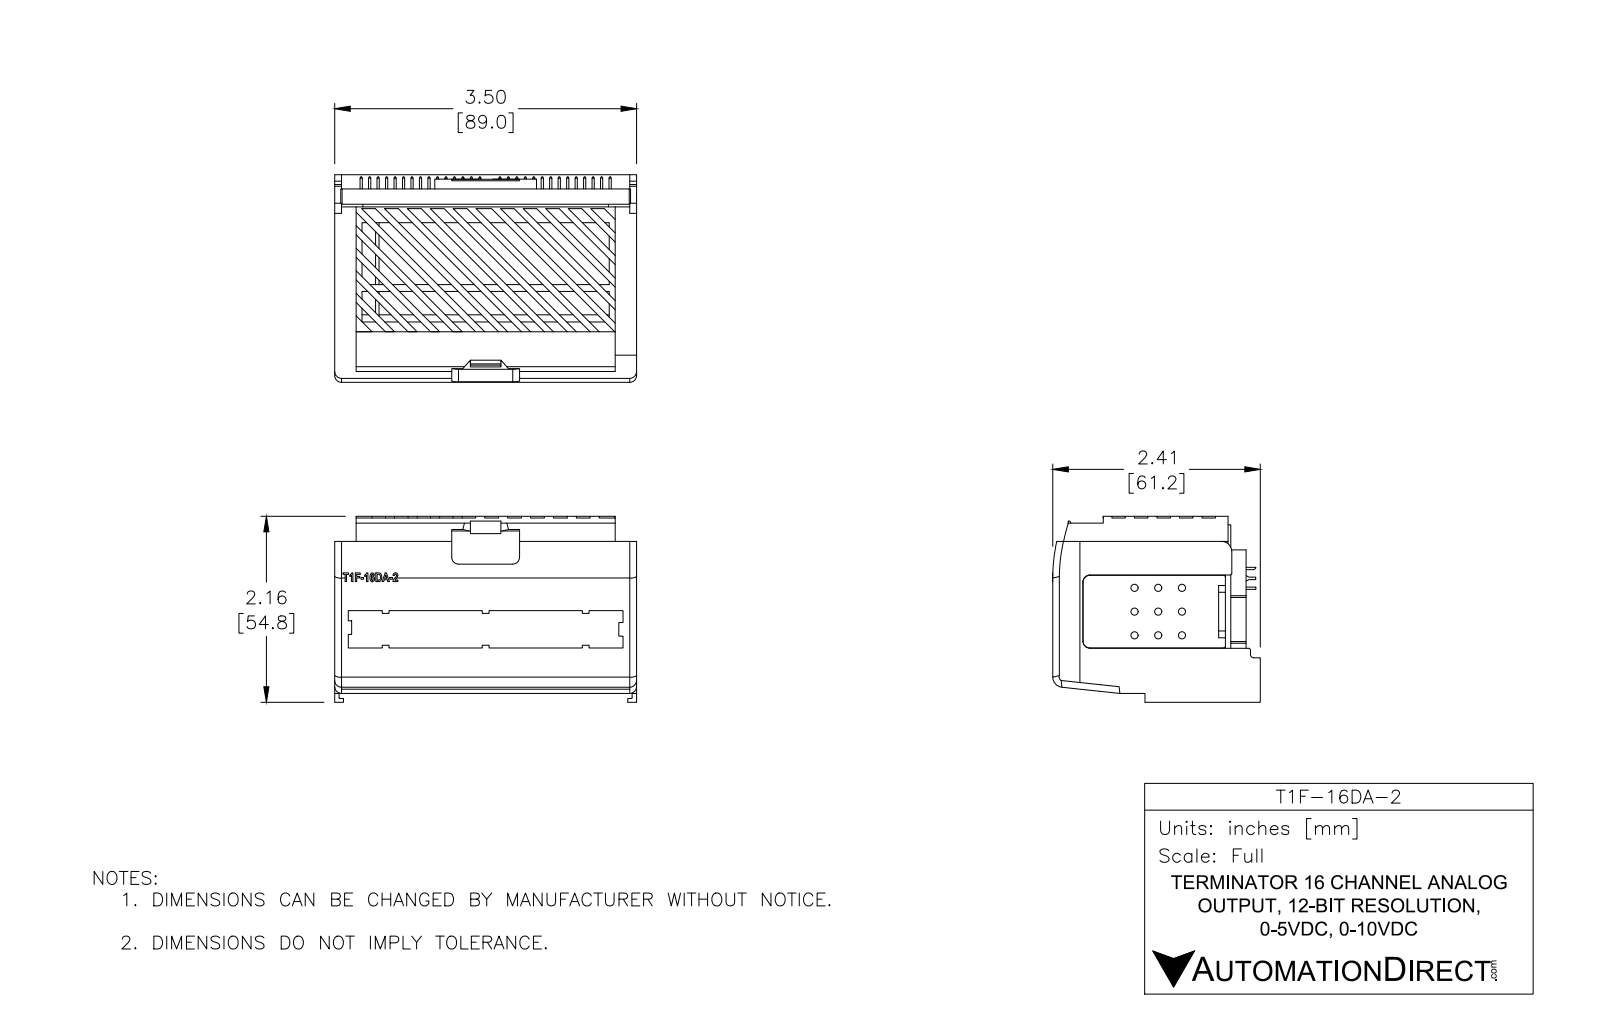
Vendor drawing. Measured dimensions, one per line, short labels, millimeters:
name: T1F-16DA-2
written by: SolidWorks 2013 (AUTOMOTIVE_DESIGN)
unit: mm
bodies: 1 solid, 653 faces (451 planar, 181 cylindrical, 21 other)
size: 88.7 × 65.1 × 61.36
volume: 45 450 mm³; area: 54 523 mm²
holes: 16× ⌀3
bosses: 56× ⌀0.7
rounds: 18× R3.5, 5× R1, 3× R0.25, 3× R0.55, 2× R1.5, 1× R8, 1× R10, 1× R18
face distances: 2, 86.7, 55.35, 0.5, 59.8, 88.7, 1.5, 55.26, 53.35, 84.7
hole spacings: 5.15, 10.3, 15.45, 20.6, 25.75, 30.9, 36.05, 41.2
